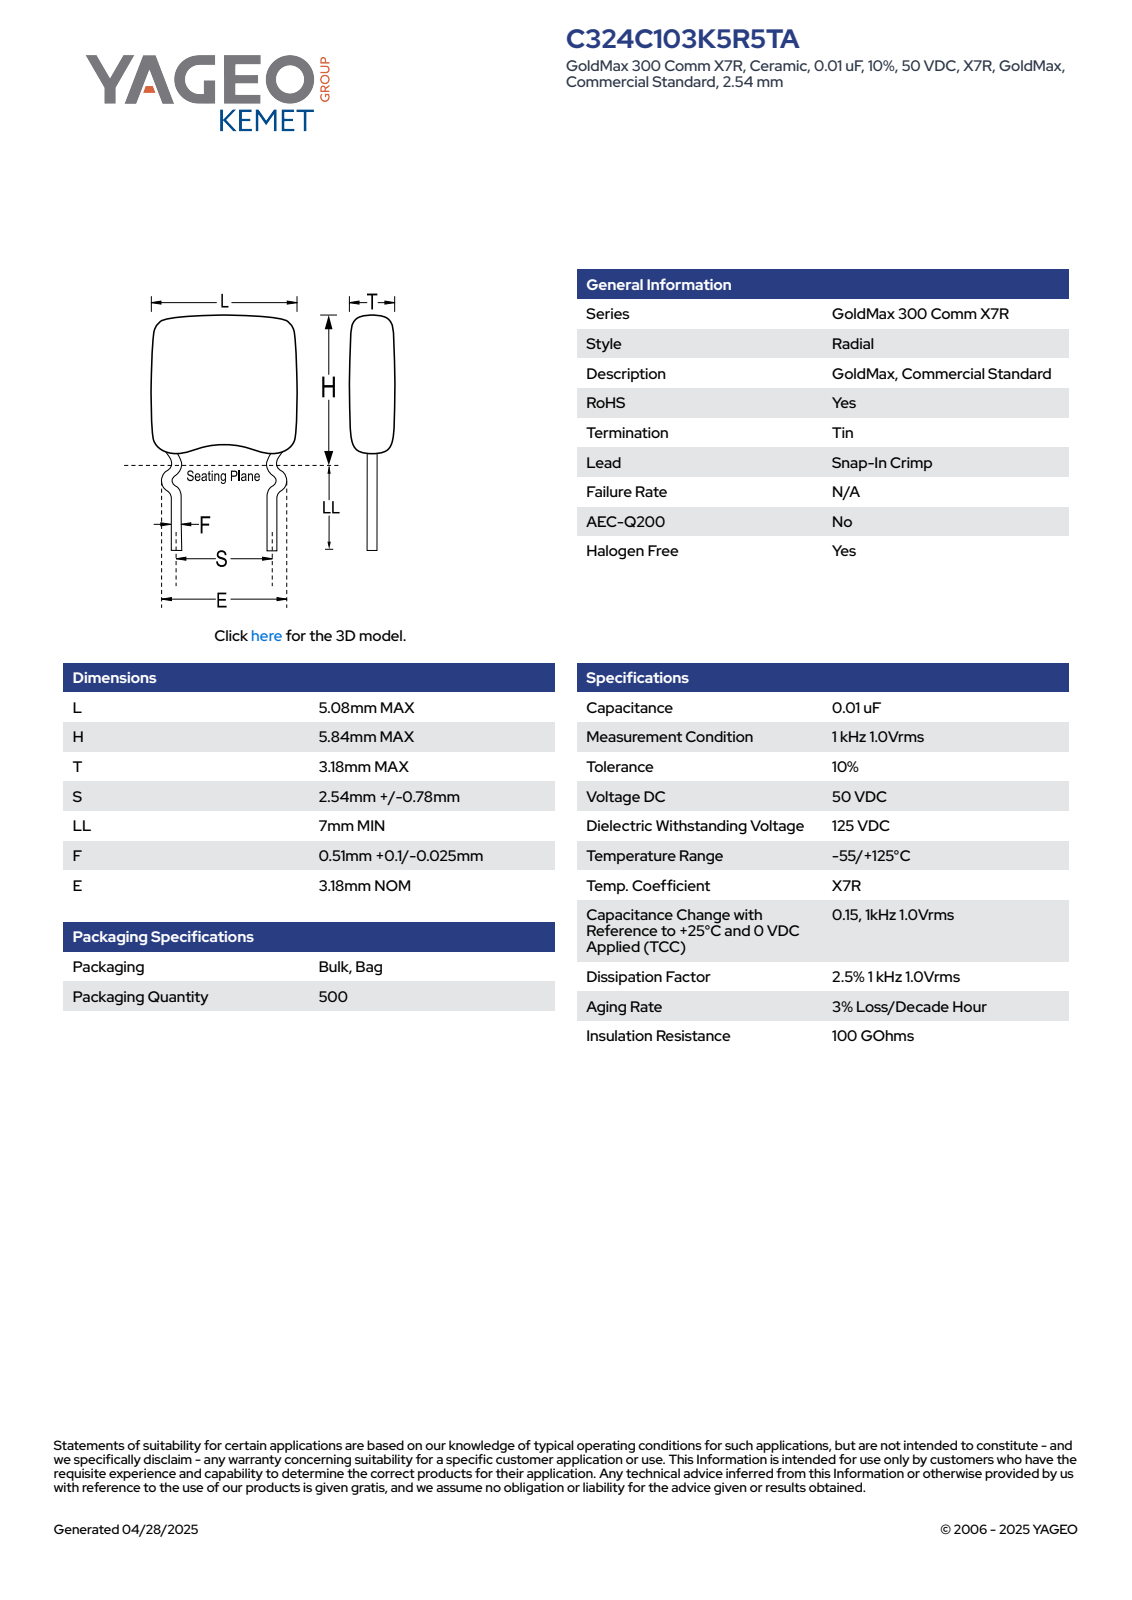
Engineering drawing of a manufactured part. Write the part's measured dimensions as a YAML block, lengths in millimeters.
part_name: "CCR_SICR2_5.08X5.84_L5.08H5.84T3.18S2.54LL7F0.51E3.18"
step_written_by: "SolidWorks 2014 (AUTOMOTIVE_DESIGN)"
units: millimeters
bodies: {solids: 4, faces: 101, planar: 65, cylindrical: 12, other: 24}
overall_size: [12.84, 5.08, 3.19]
volume: 71
surface_area: 116
partial_cylinders:
  - {radius: 1, count: 12}
face_to_face_distances: [3.18, 5.08, 4.81, 3.19, 8.03, 12.84, 10.16, 2.13, 2.68, 2.37]
